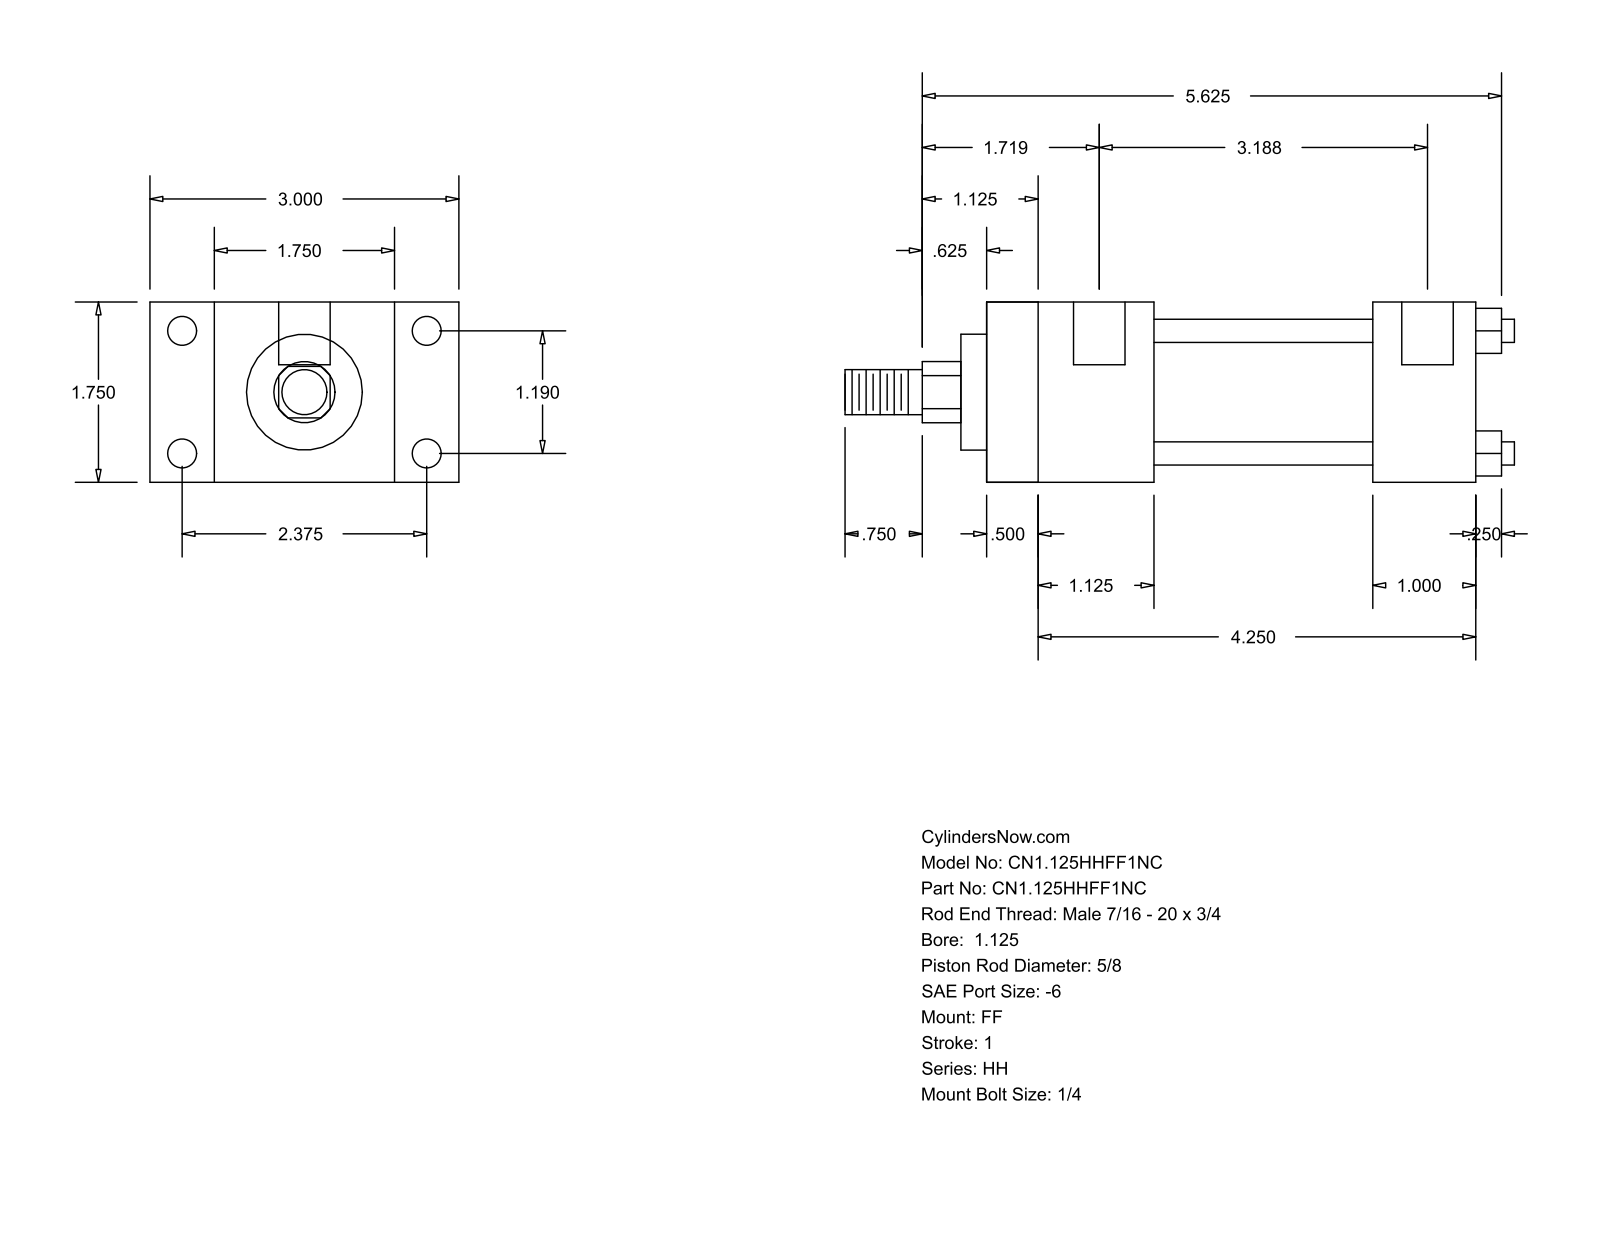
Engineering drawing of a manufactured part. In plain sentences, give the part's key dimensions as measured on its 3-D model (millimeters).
The part is named "HH_FF__0112_0.625". Its 3-D file was written by "GSSL Pune (CONFIG_CONTROL_DESIGN)". It is 0 solids with 92 faces: 64 planar, 28 cylindrical and 0 other. Overall it measures 165.1 by 76.2 by 44.45 millimeters. Round holes: 4 of diameter 5.56, 4 of diameter 7.14, 2 of diameter 12.7. Round bosses or shafts: 4 of diameter 5.71, 1 of diameter 34.92, 1 of diameter 28.57, 1 of diameter 15.88, 1 of diameter 11.11. Partial cylindrical surfaces (rounded edges, fillets, slot ends): 1 of radius 7.54. The main face-to-face distances are 44.46, 120.65, 15.87, 12.69, 107.96, 28.58, 60.33, 41.27, 95.24, 82.55. The hole center spacings are 30.22, 60.32, 67.47, 77.79, 3.17, 80.96.
